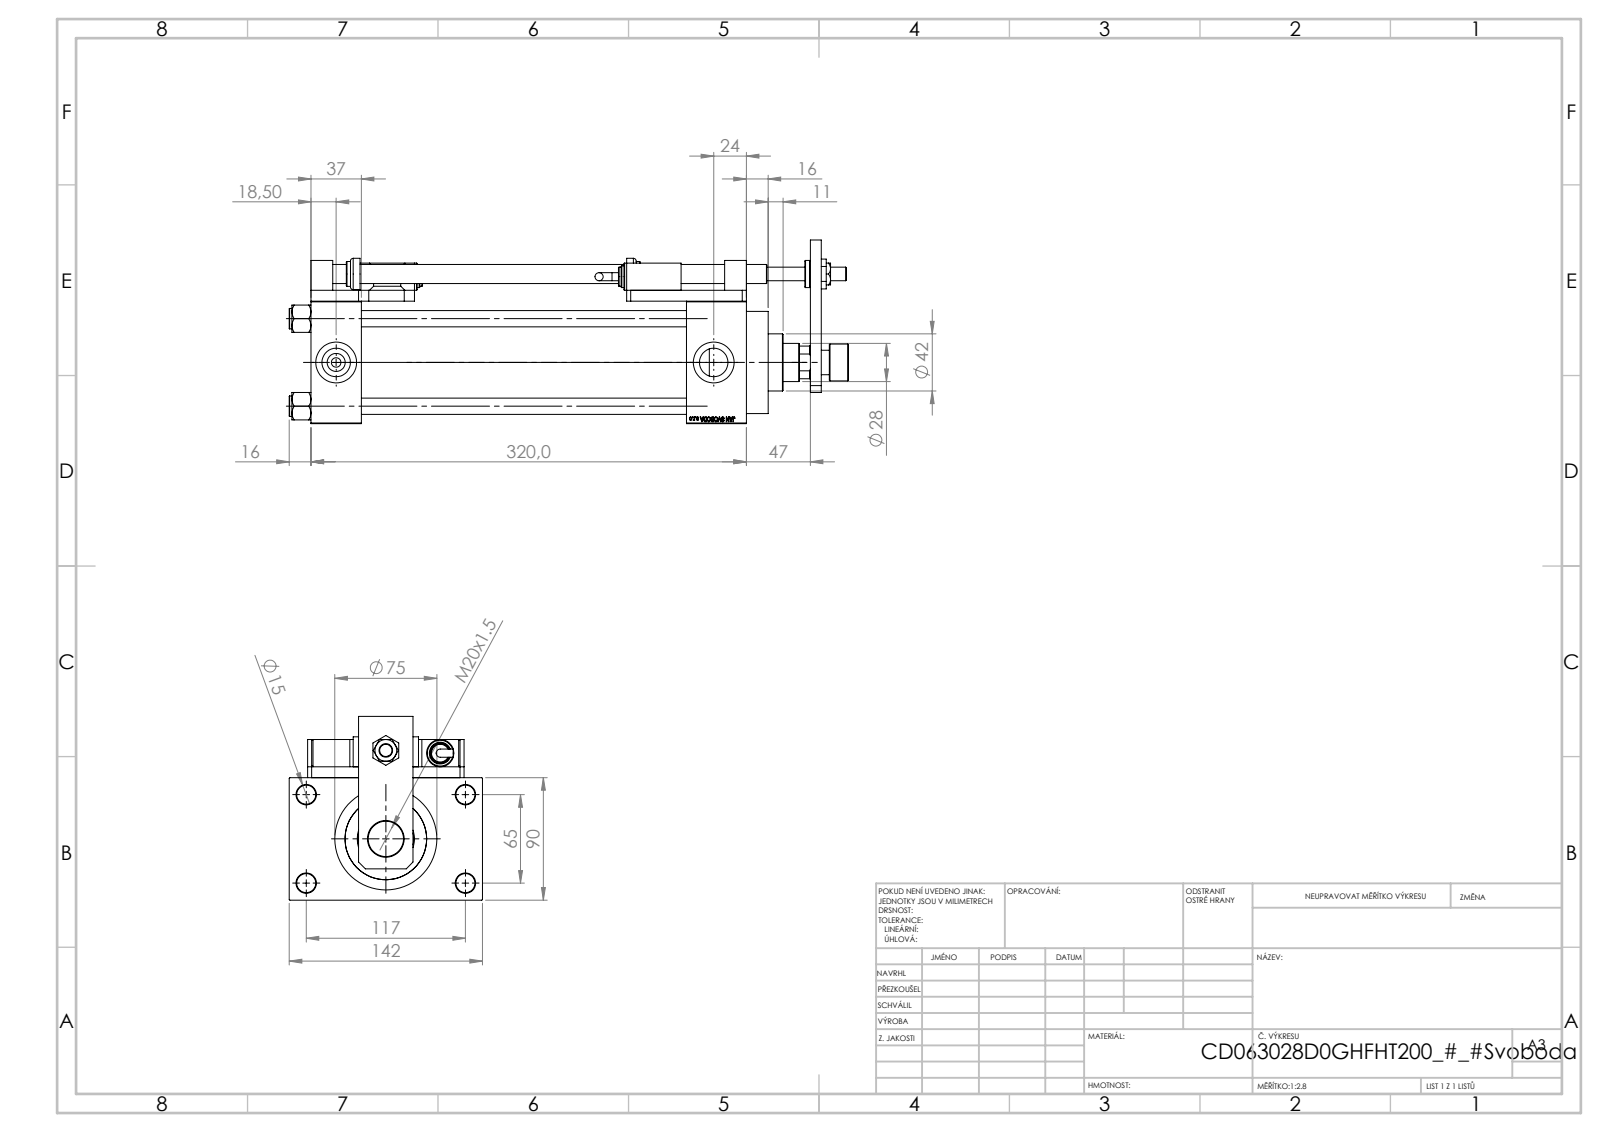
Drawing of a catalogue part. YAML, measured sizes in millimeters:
part_name: "V215CD_SWITCH_Q_PODLOZKA_FRONT; V215CD_NUT_M5_D; V215CD_SWITCH_Q_BLOK; V215CD_SWITCH_Q_MAGNET (+7 more)"
step_written_by: "SolidWorks 2019 (CONFIG_CONTROL_DESIGN)"
units: millimeters
bodies: {solids: 25, faces: 1345, planar: 622, cylindrical: 160, other: 563}
overall_size: [411, 142, 135]
volume: 1705000
surface_area: 414349
round_holes:
  - {diameter: 14, count: 5}
  - {diameter: 8.5, count: 4}
  - {diameter: 12, count: 4}
  - {diameter: 13.5, count: 4}
  - {diameter: 7, count: 2}
  - {diameter: 20.96, count: 2}
  - {diameter: 30, count: 2}
  - {diameter: 10, count: 1}
  - {diameter: 18.5, count: 1}
  - {diameter: 20, count: 1}
  - {diameter: 28, count: 1}
  - {diameter: 31, count: 1}
round_bosses_or_shafts:
  - {diameter: 15, count: 4}
  - {diameter: 20, count: 3}
  - {diameter: 16, count: 2}
  - {diameter: 14, count: 2}
  - {diameter: 6, count: 2}
  - {diameter: 75, count: 1}
  - {diameter: 69, count: 1}
  - {diameter: 42, count: 1}
partial_cylinders:
  - {radius: 7.5, count: 4}
face_to_face_distances: [8, 90, 44, 320, 37, 98, 283, 276, 239, 47]
hole_center_spacings: [66.92, 26.35, 45.47, 64.3, 69.81, 90.65, 111.34, 65]
